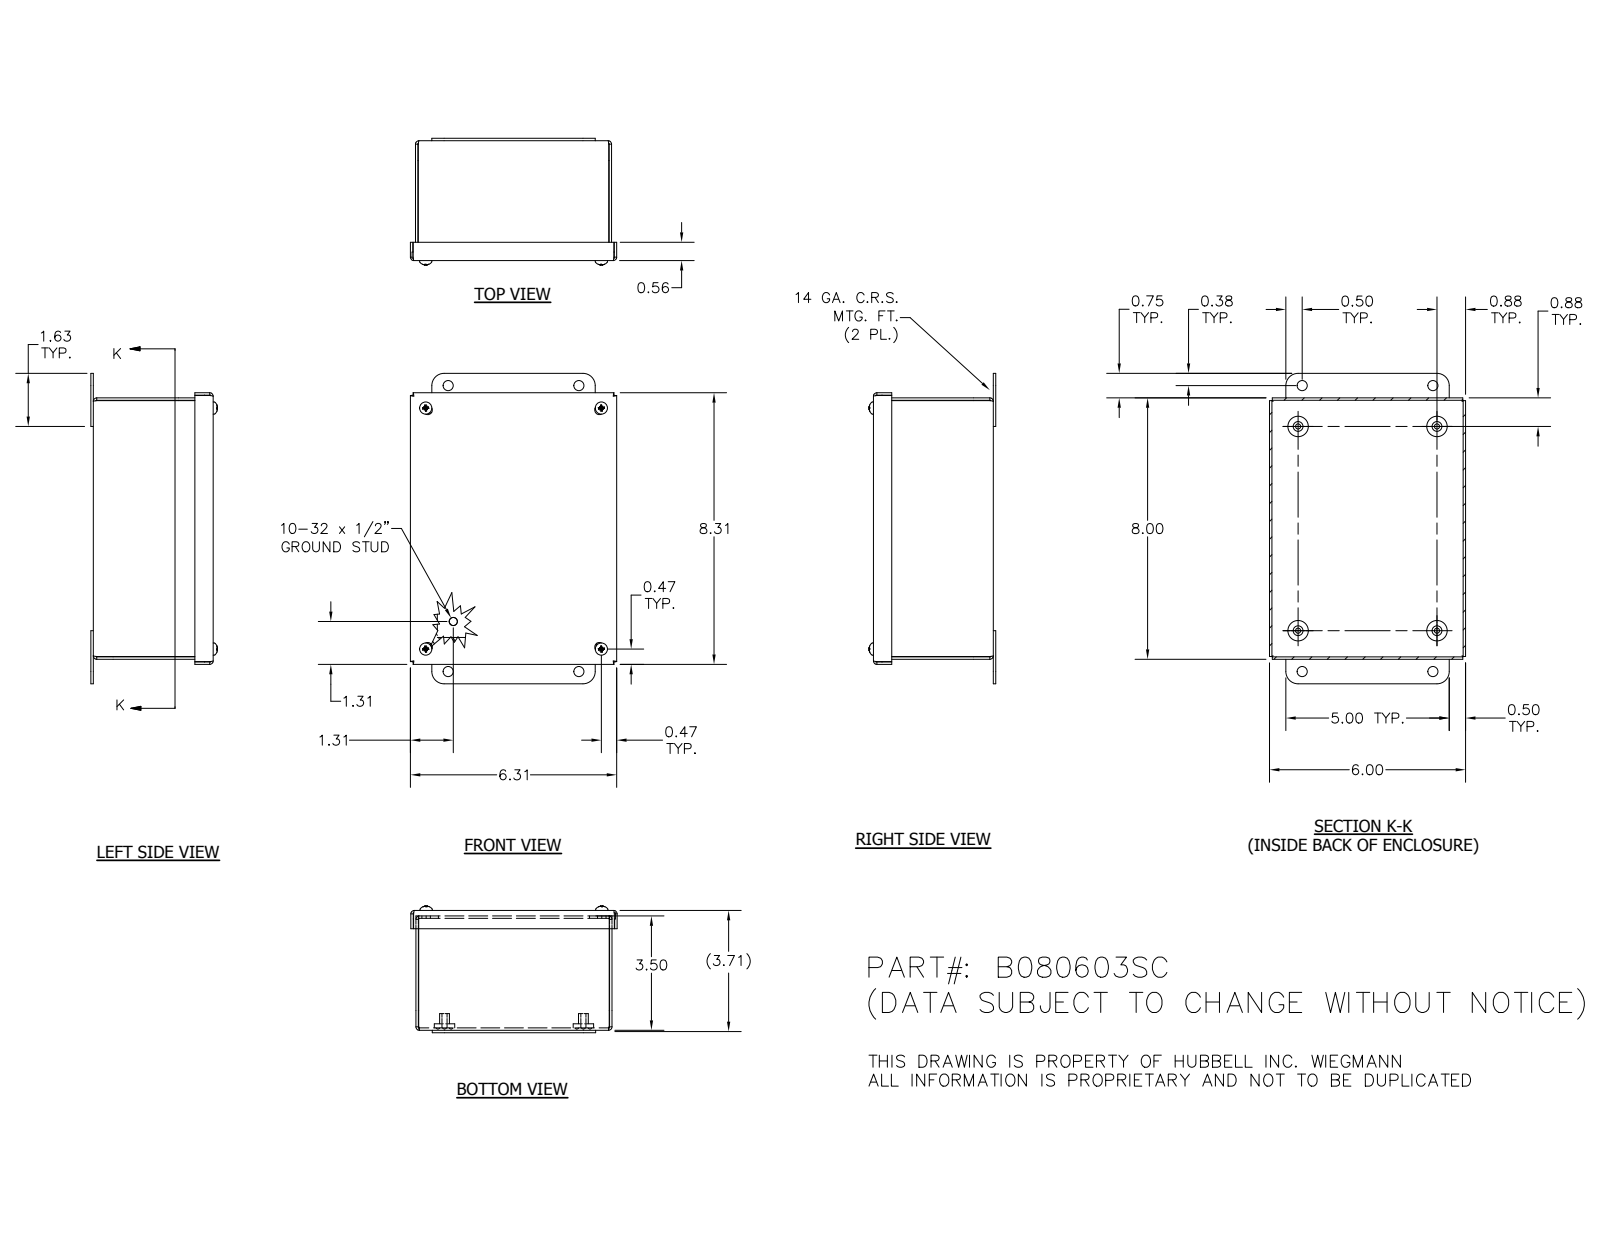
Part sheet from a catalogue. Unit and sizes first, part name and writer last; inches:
Units: inches
Overall size (bounding box): 9.5 × 6.313 × 3.346
Round holes (diameter × count): ⌀0.145 ×4, ⌀0.156 ×4, ⌀0.196 ×4, ⌀0.278 ×4, ⌀0.281 ×4, ⌀0.31 ×4, ⌀0.313 ×4
Round bosses / shafts (diameter × count): ⌀0.19 ×5, ⌀0.625 ×4, ⌀0.453 ×4, ⌀0.406 ×4, ⌀0.373 ×4, ⌀0.3 ×4, ⌀0.248 ×4, ⌀0.25 ×1
Partial cylindrical surfaces — rounded edges, fillets, slot ends (radius × count): R0.031 ×12, R0.105 ×12, R0.089 ×4, R0.375 ×4
Main face-to-face distances: 0.074, 3.094, 3.168, 3.02, 5.926, 7.926, 5.852, 6, 0.187, 2.906
Hole centre spacings: 5.314, 7.314, 7.395, 0.087, 7.333, 9.04, 0.795, 0.796
Volume: 19.87 in³ · Surface area: 500.9 in²
Bodies: 23 solids, 532 faces (311 planar, 102 cylindrical, 119 other)
Part name (STEP PRODUCT): B080603SC; 3482; 34984; B080603SCBKP (+6 more)
STEP written by: Autodesk Inventor 2012 (AUTOMOTIVE_DESIGN)
